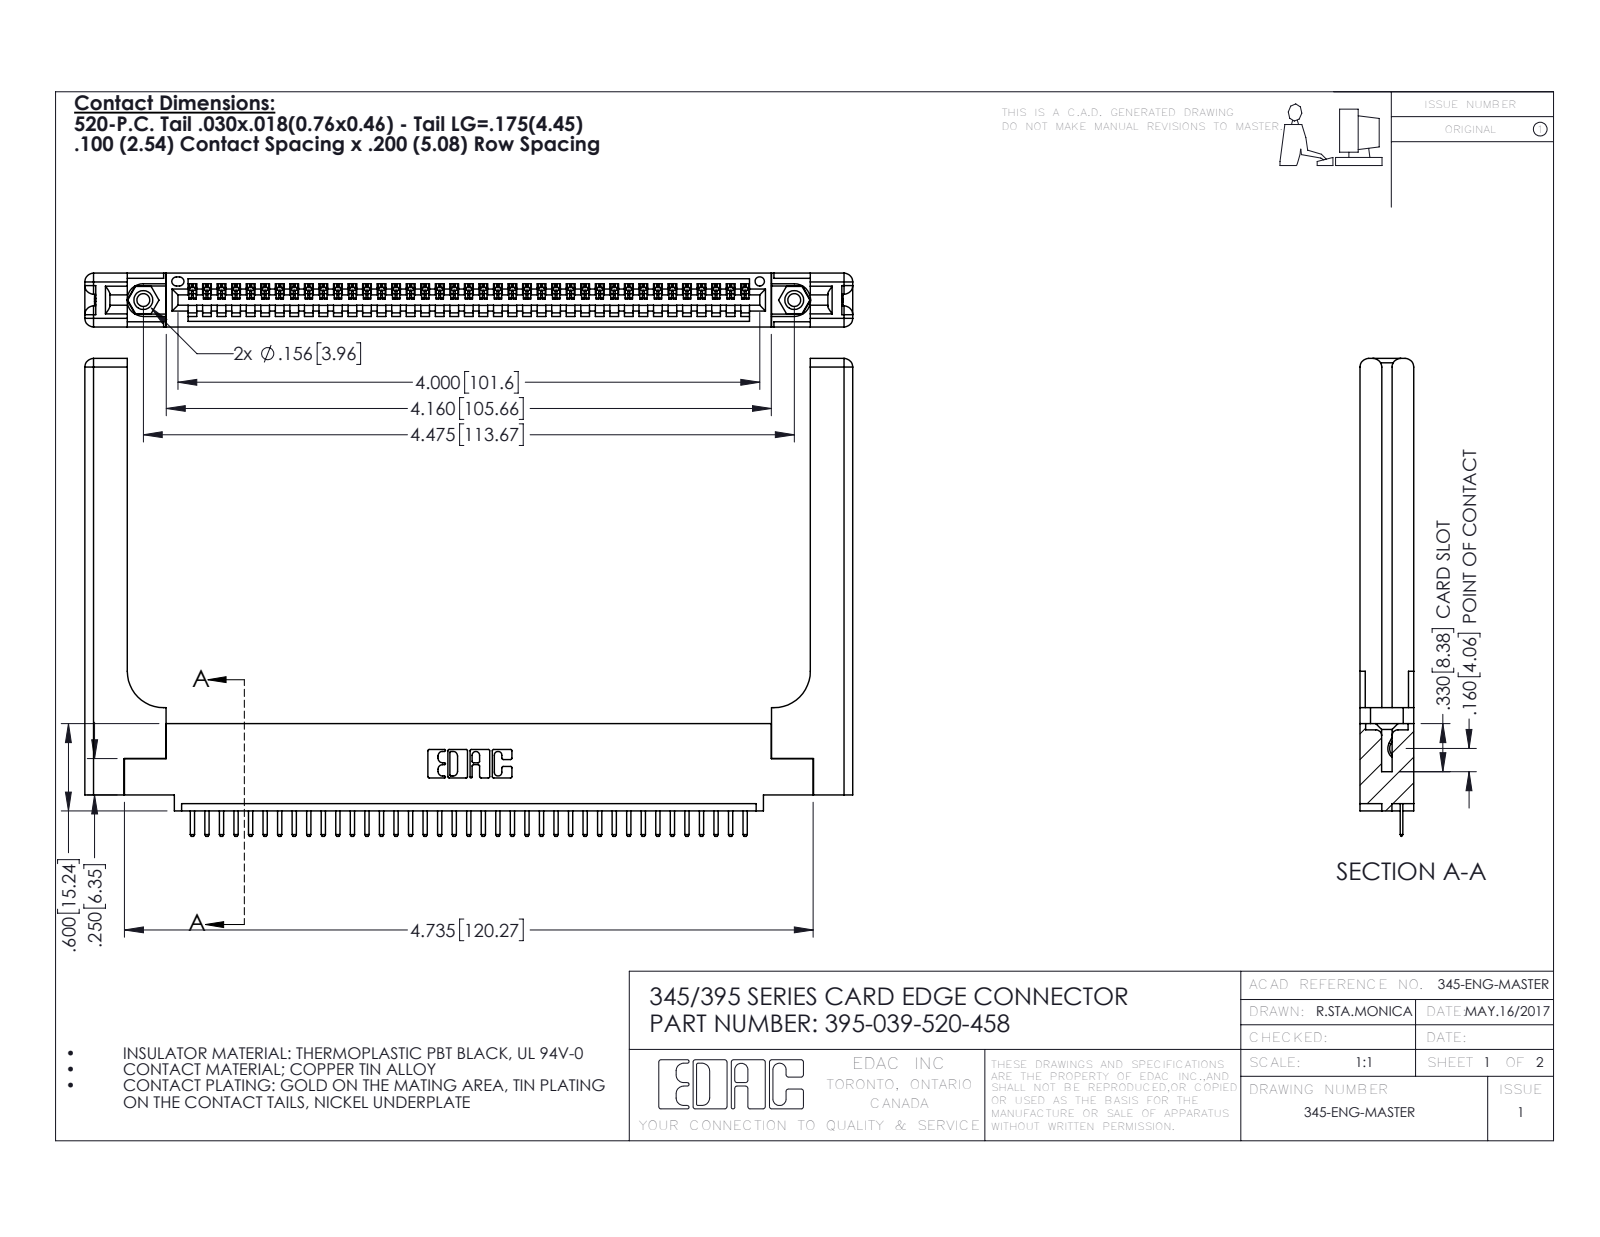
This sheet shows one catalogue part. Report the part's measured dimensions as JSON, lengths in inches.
{"part_name": "345 Part_0.110 Offset - 0.156 Dia-TH; 345-220-058_345-220-058; 345-292-001_345-293-120; 345-250-001_345-250-001-102 (+1 more)", "step_written_by": "SolidWorks 2016 (CONFIG_CONTROL_DESIGN)", "units": "inches", "bodies": {"solids": 44, "faces": 2804, "planar": 1870, "cylindrical": 874, "other": 60}, "overall_size": [5.279, 3.285, 0.37], "volume_in3": 1.283, "surface_area_in2": 33.52, "round_holes": [[0.089, 2], [0.125, 2], [0.156, 2], [0.064, 1]], "round_bosses_or_shafts": [[0.155, 2]], "partial_cylinders_radius": [[0.01, 80], [0.006, 78], [0.01, 22], [0.06, 16], [0.007, 6], [0.031, 6], [0.026, 3], [0.03, 2]], "face_to_face_distances": [0.37, 0.072, 0.298, 0.2, 0.098, 0.272, 0.025, 0.148, 0.15, 0.225], "hole_center_spacings": [0.27, 4.239, 4.475]}
